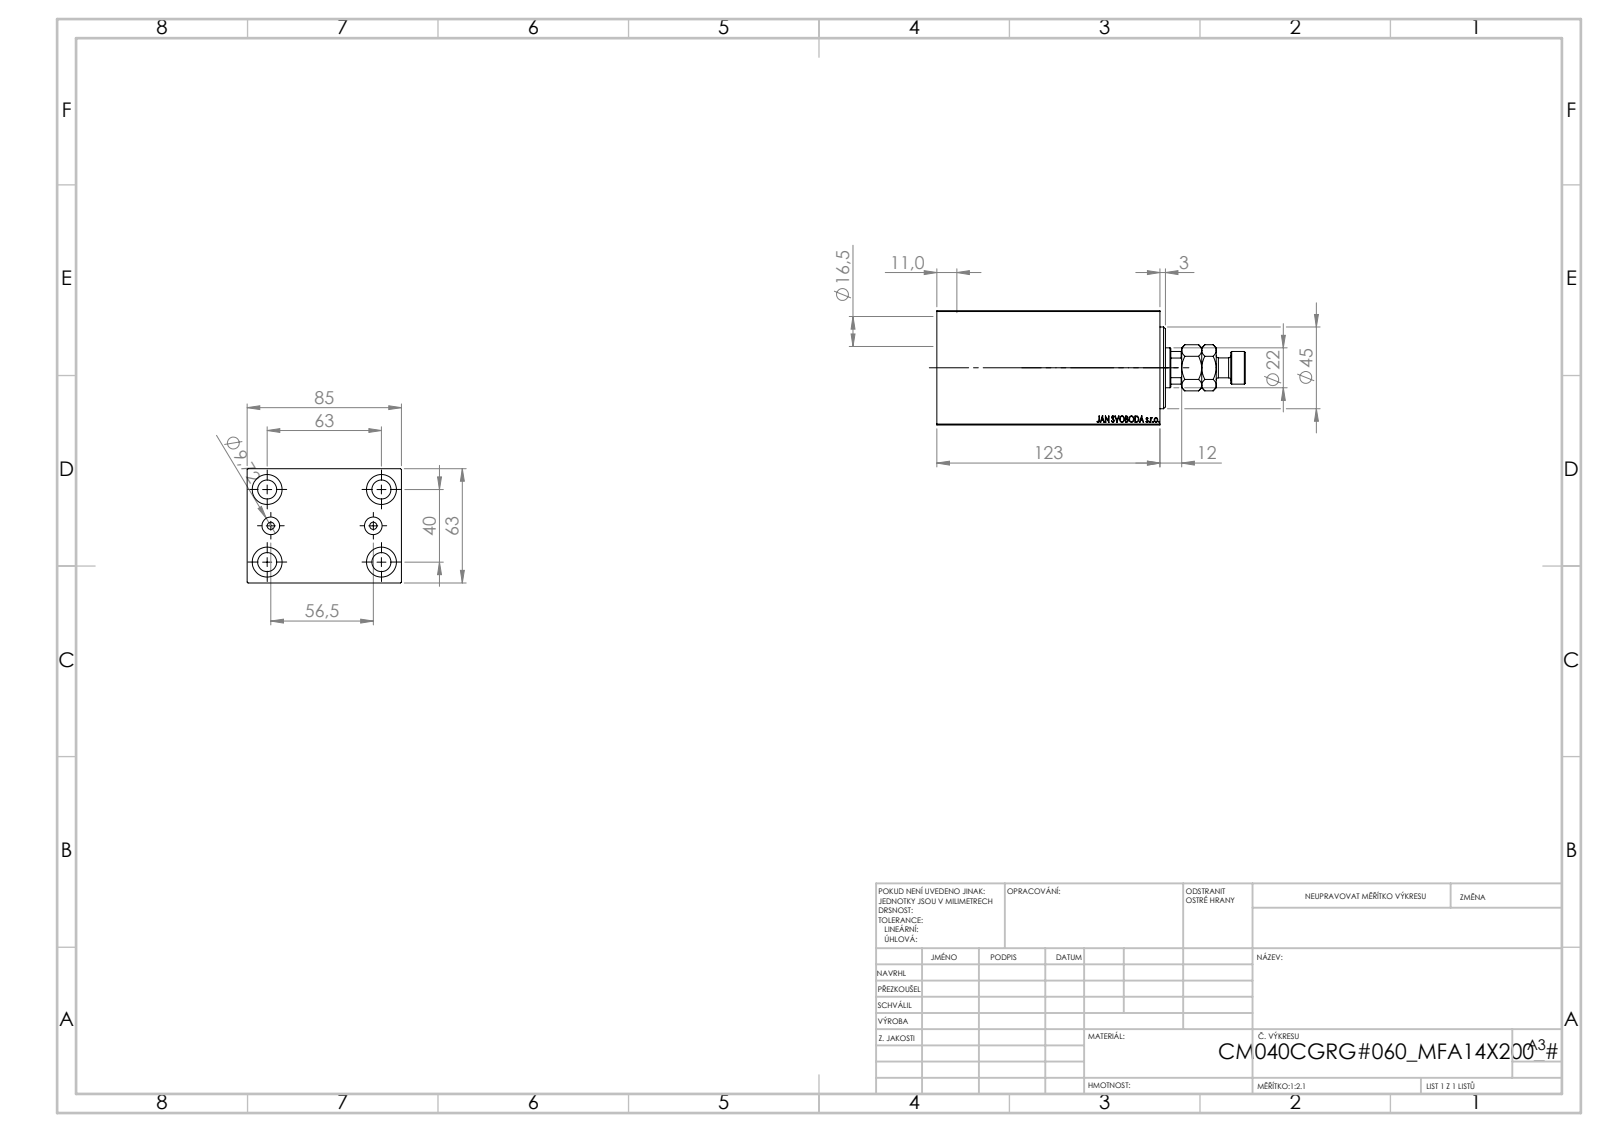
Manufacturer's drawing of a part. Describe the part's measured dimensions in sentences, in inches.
The part is named "V450CM_VC_B; V450CM_C_Body; V450CM_C_VCP; MFA". Its 3-D file was written by "SolidWorks 2019 (CONFIG_CONTROL_DESIGN)". It is 4 solids with 910 faces: 424 planar, 60 cylindrical and 426 other. Overall it measures 6.693 by 3.346 by 2.48 inches. Its volume is 34.39 cubic inches and its surface area 152.2 square inches. Round holes: 4 of diameter 0.413, 4 of diameter 0.65, 2 of diameter 0.157, 2 of diameter 0.383, 1 of diameter 0.492, 1 of diameter 0.866, 1 of diameter 1.004, 1 of diameter 1.575, 1 of diameter 1.654, 1 of diameter 1.772. Round bosses or shafts: 1 of diameter 0.709, 1 of diameter 0.433. Partial cylindrical surfaces (rounded edges, fillets, slot ends): 1 of radius 0.413. The main face-to-face distances are 2.48, 3.346, 4.843, 3.474, 1.368, 0.394, 4.449, 0.866, 3.081, 0.433. The hole center spacings are 0.798, 1.469, 2.481, 1.112, 1.575, 2.48, 2.938, 2.224.
